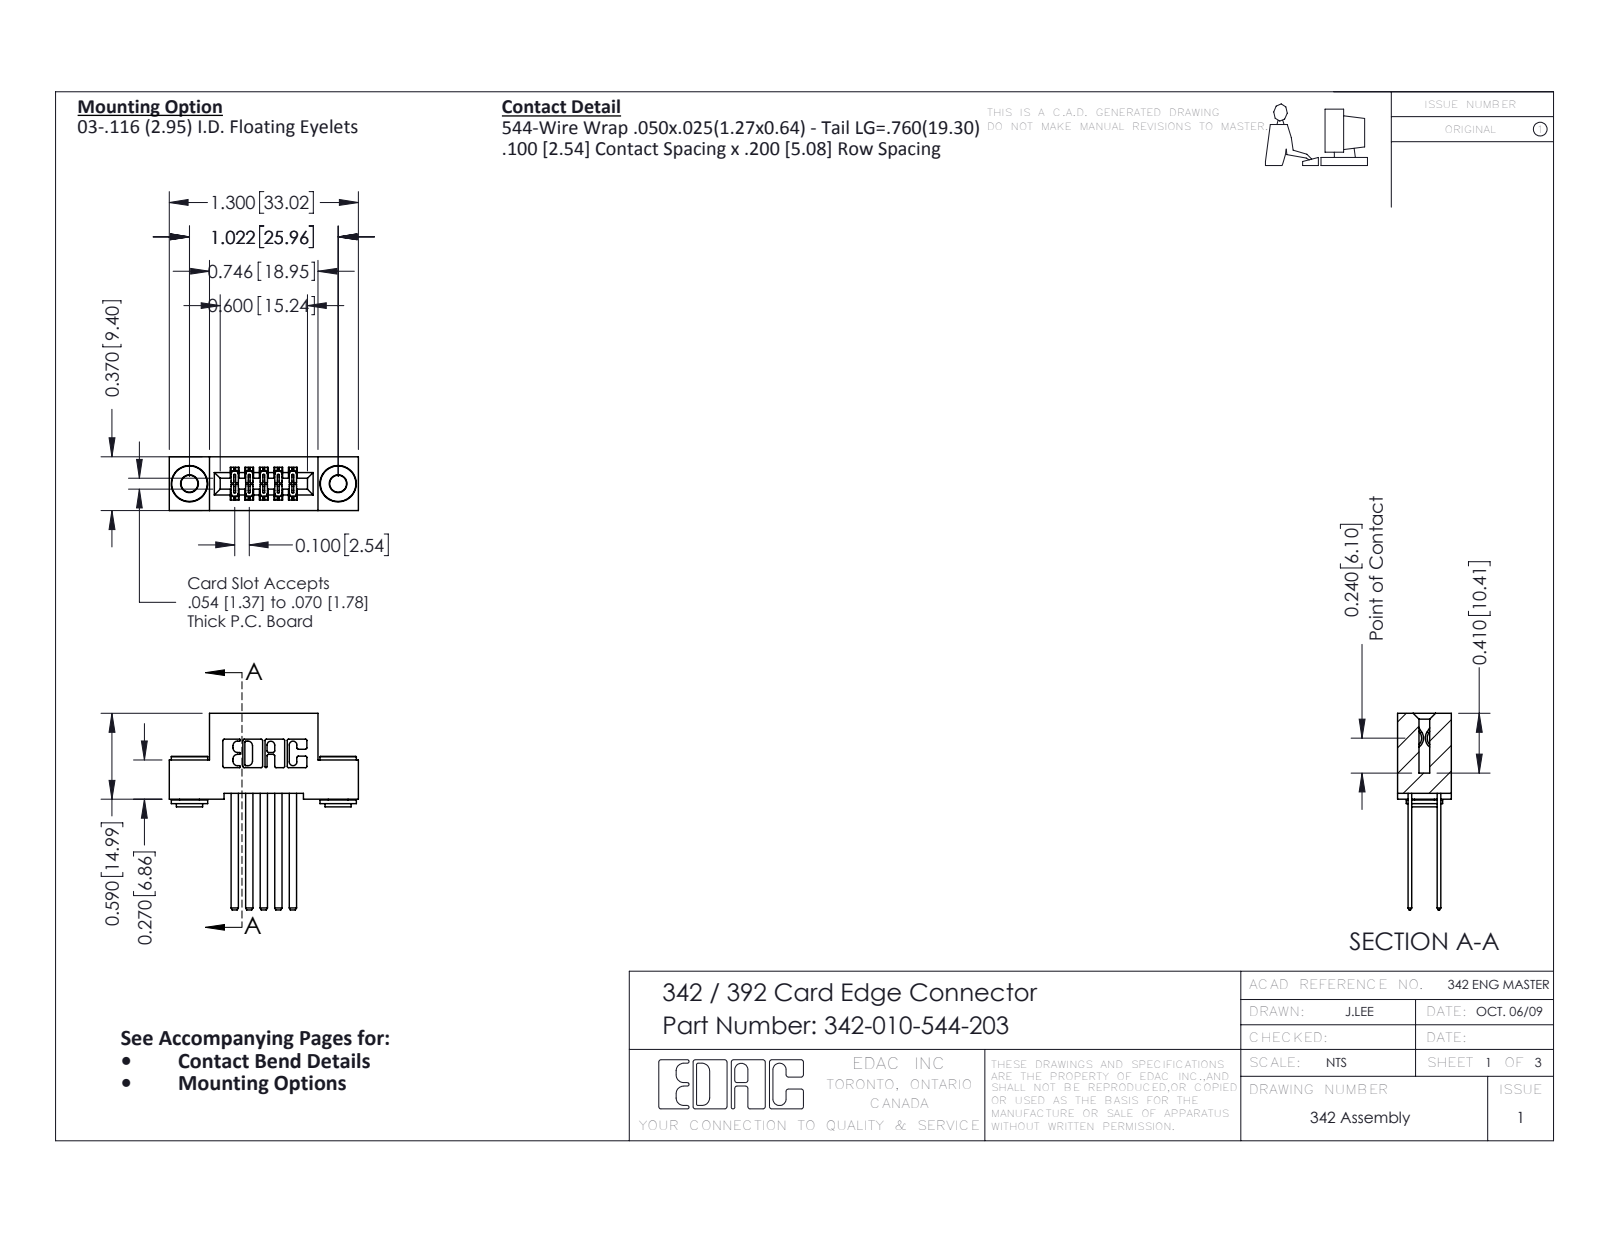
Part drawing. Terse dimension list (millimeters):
name: 342-010-544-203; 342 Part_.156 TH; 342-250-002_345-250-002-102; 345-292-001_345-293-144
written by: SolidWorks 2016 (CONFIG_CONTROL_DESIGN)
unit: mm
bodies: 13 solids, 608 faces (396 planar, 204 cylindrical, 8 other)
size: 34.3 × 33 × 9.4
volume: 2 950 mm³; area: 4 500 mm²
holes: 2× ⌀2.9, 2× ⌀4
bosses: 2× ⌀6.4, 2× ⌀4.6, 2× ⌀3.5
rounds: 22× R0.3, 15× R0.2, 6× R0.2, 6× R0.8, 3× R0.7, 2× R0.4, 2× R0.6, 2× R0.6
face distances: 5.1, 1.8, 7.6, 2.5, 2.5, 6.9, 0.6, 9.4, 1, 7.6
hole spacings: 26
